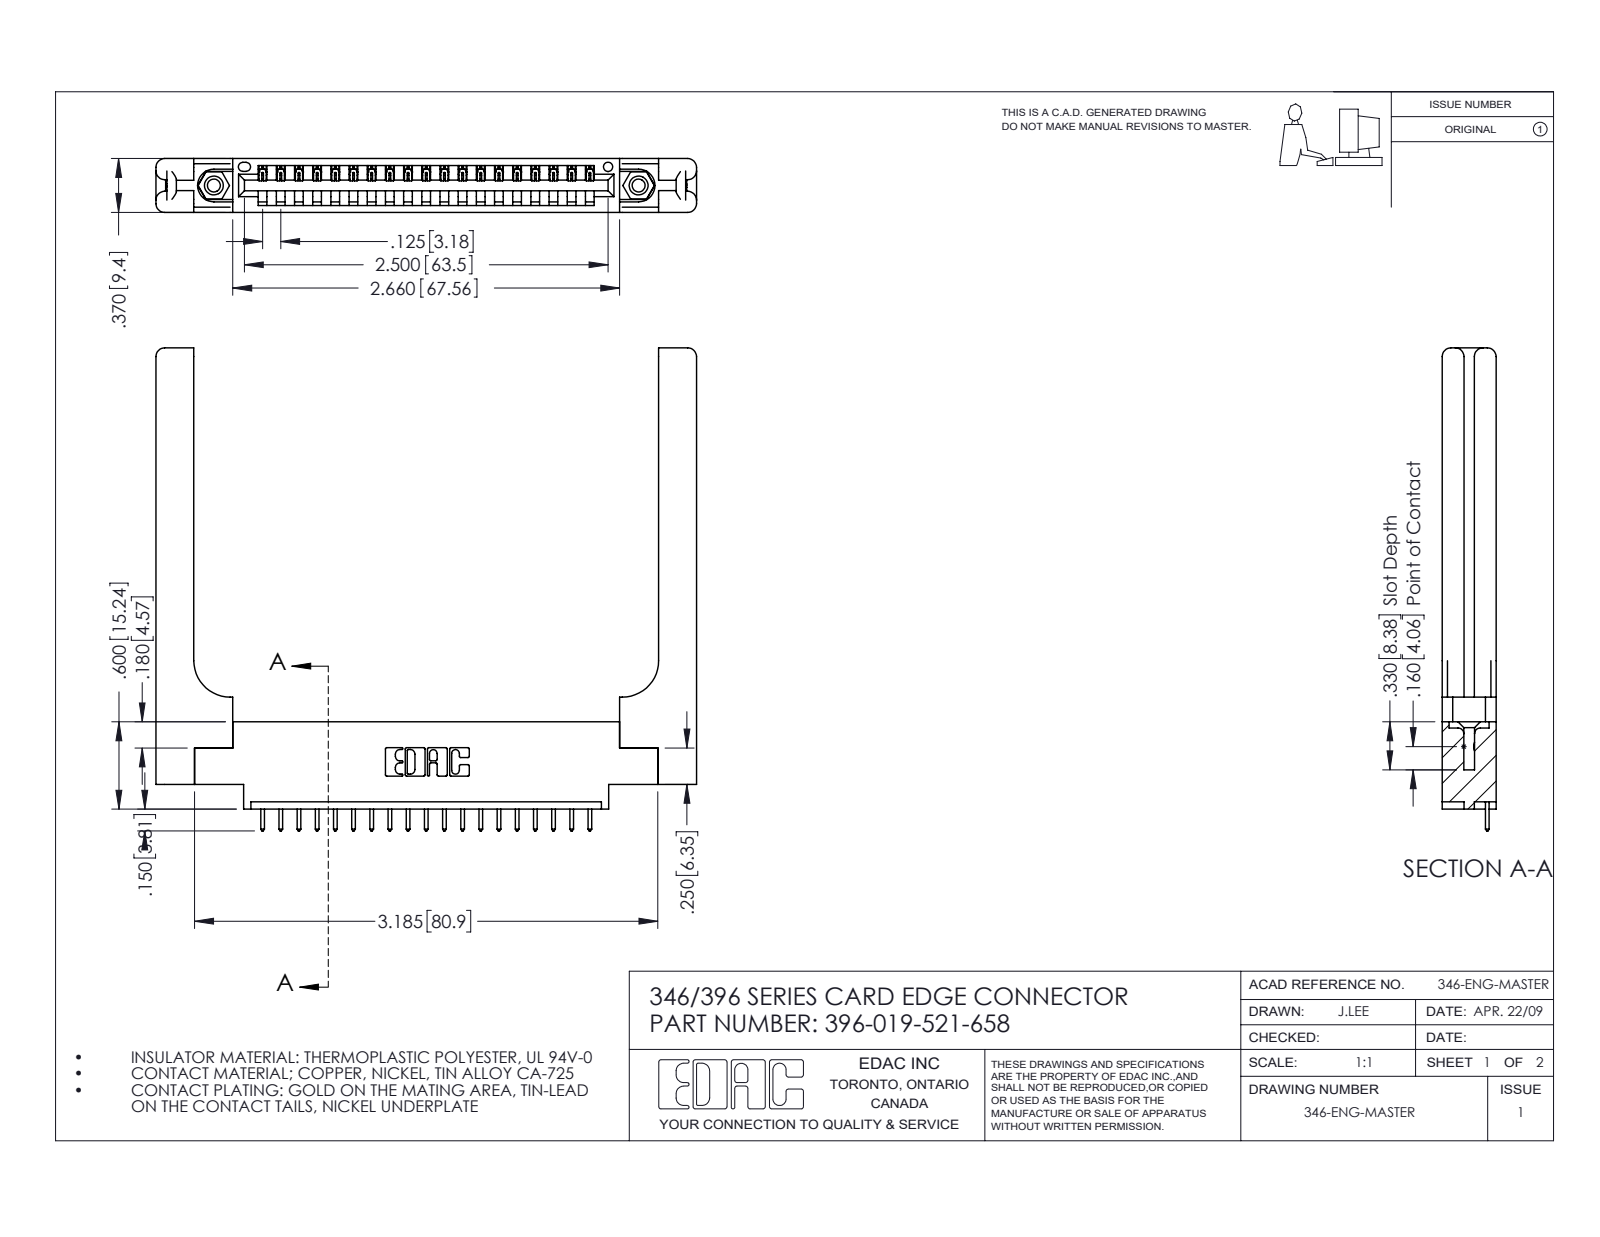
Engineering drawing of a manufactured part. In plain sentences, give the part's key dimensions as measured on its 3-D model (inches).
The part is named "346-220-058_345-220-058; 345-250-001_345-250-001-102; 345-292-001_345-293-121; 396-019-521-658 (+1 more)". Its 3-D file was written by "SolidWorks 2016 (CONFIG_CONTROL_DESIGN)". It is 24 solids with 1484 faces: 988 planar, 436 cylindrical and 60 other. Overall it measures 3.716 by 3.32 by 0.37 inches. Its volume is 0.988 cubic inches and its surface area 24.34 square inches. Round holes: 2 of diameter 0.089, 2 of diameter 0.125, 2 of diameter 0.156, 1 of diameter 0.064. Round bosses or shafts: 2 of diameter 0.155. Partial cylindrical surfaces (rounded edges, fillets, slot ends): 38 of radius 0.006, 38 of radius 0.01, 22 of radius 0.01, 16 of radius 0.06, 6 of radius 0.007, 6 of radius 0.031, 3 of radius 0.026, 2 of radius 0.03. The main face-to-face distances are 0.37, 0.15, 0.072, 0.148, 0.048, 0.322, 0.25, 0.102, 0.22, 0.173. The hole center spacings are 0.246, 2.713, 2.92.
